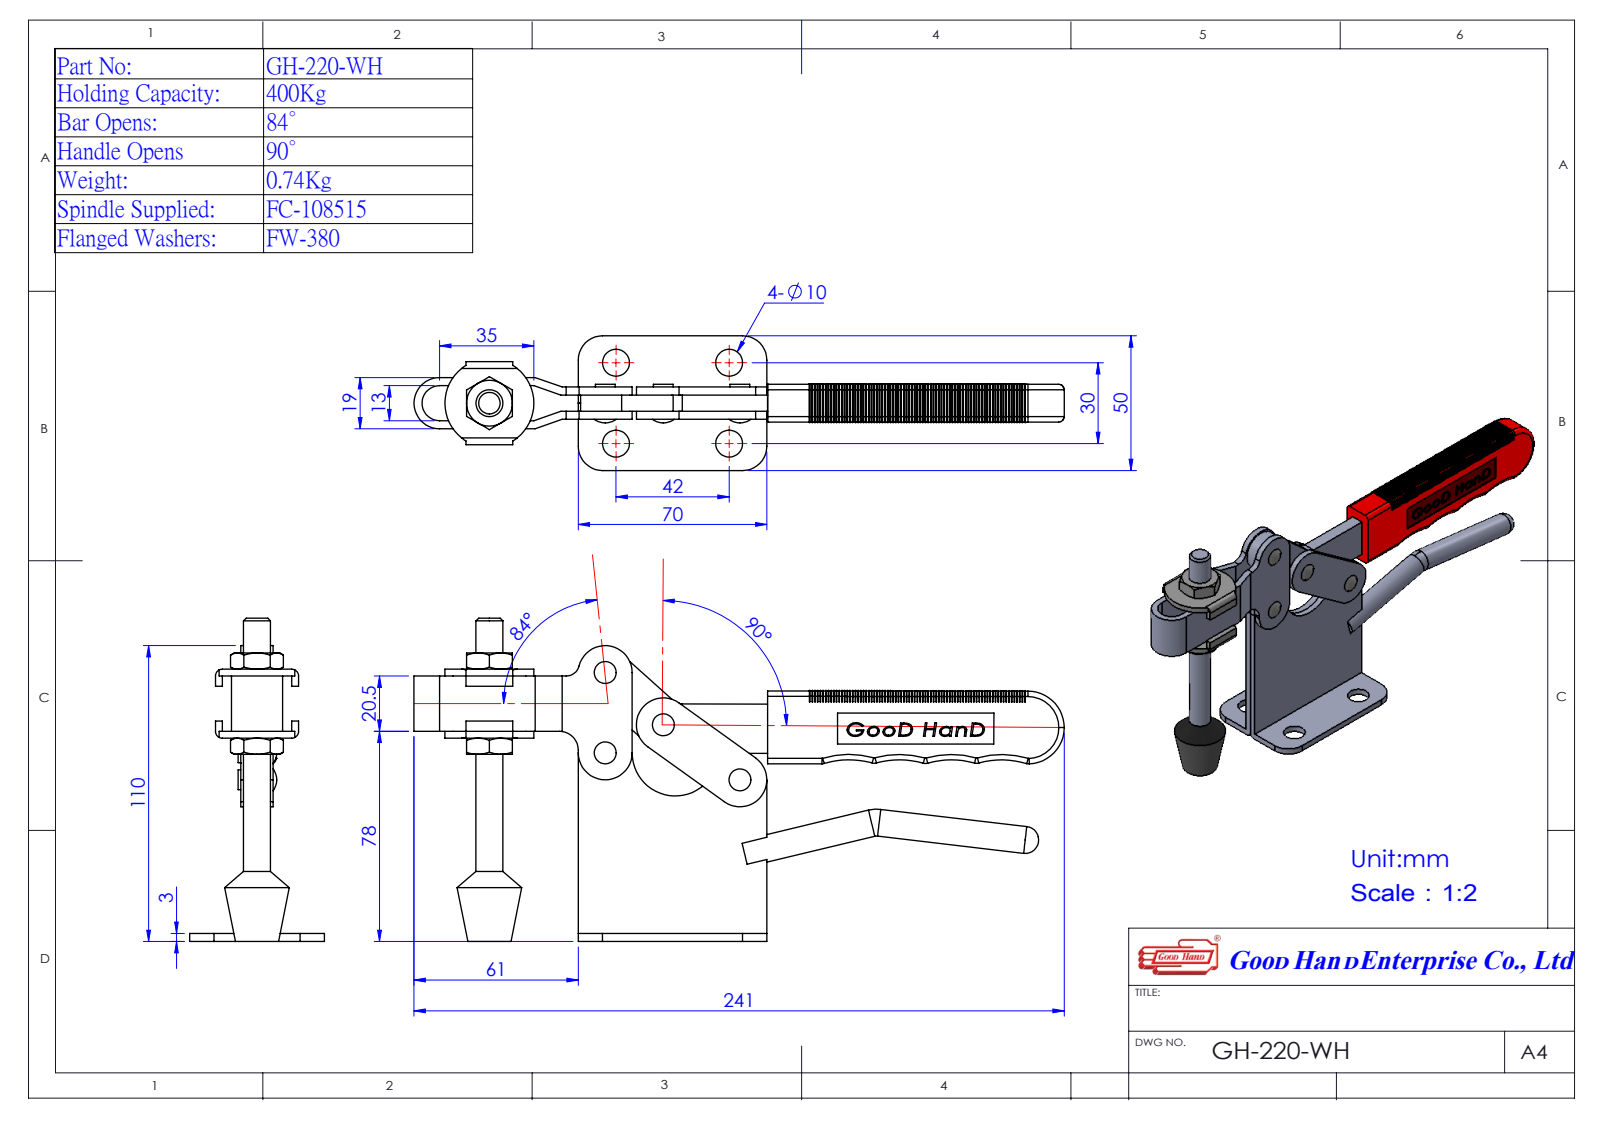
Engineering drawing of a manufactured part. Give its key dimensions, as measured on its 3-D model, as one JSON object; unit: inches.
{"part_name": "Group5^GH-220-WLH; Group3^GH-220-WH; Group2^GH-220-WH; Group1^GH-220-WH (+1 more)", "step_written_by": "SolidWorks 2016 (AUTOMOTIVE_DESIGN)", "units": "inches", "bodies": {"solids": 6, "faces": 245, "planar": 101, "cylindrical": 102, "other": 42}, "overall_size": [9.504, 4.5, 1.969], "volume_in3": 7.969, "surface_area_in2": 89.92, "round_holes": [[0.197, 4], [0.394, 4], [0.249, 2]], "round_bosses_or_shafts": [[0.289, 4], [0.394, 2], [0.787, 1], [0.375, 1]], "partial_cylinders_radius": [[0.118, 5], [0.354, 5], [0.1, 4], [1.26, 4], [0.394, 3], [0.197, 2], [0.256, 1], [0.276, 1]], "face_to_face_distances": [0.118, 0.236, 0.157, 0.394, 0.512, 0.039, 0.354, 0.138, 0.492, 0.02], "hole_center_spacings": [1.181, 1.654, 2.032, 0.943, 1.142, 1.173, 1.378, 2.007]}
